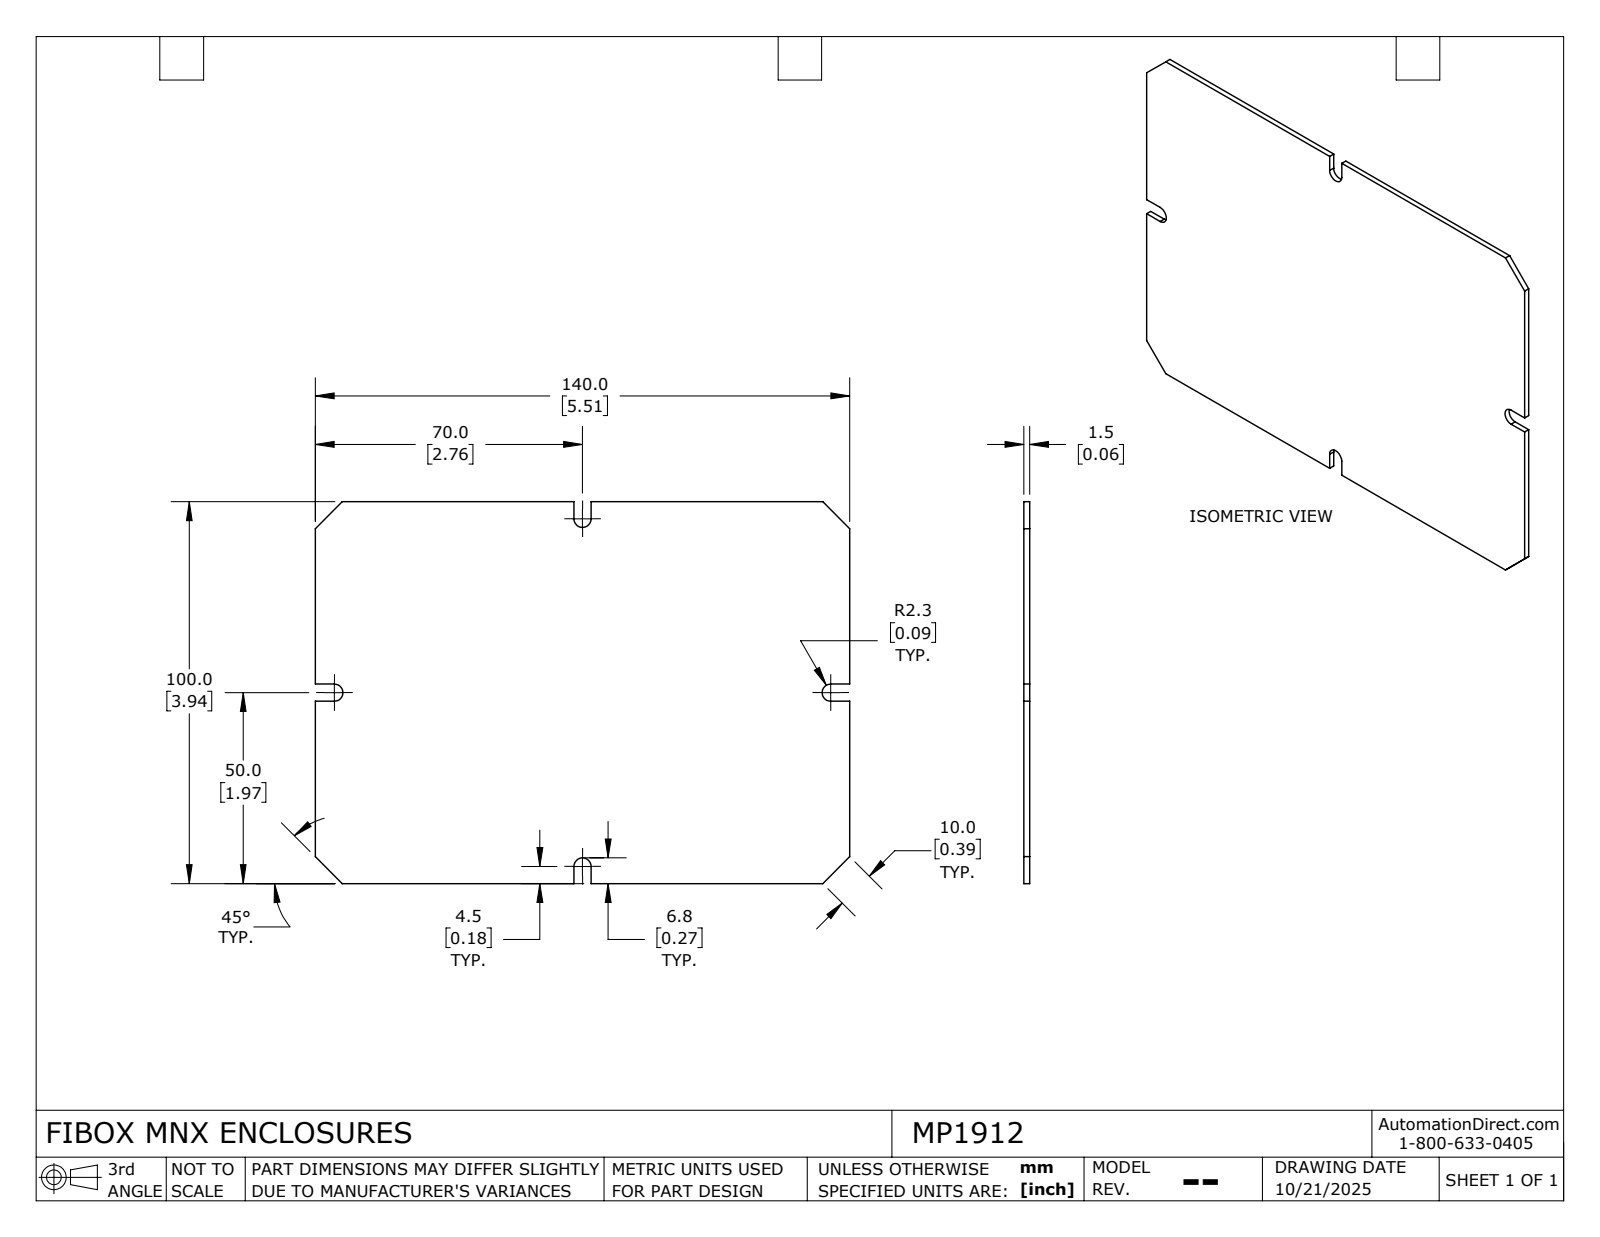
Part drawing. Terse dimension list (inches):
name: MP1912_Default
written by: SolidWorks 2024 (CONFIG_CONTROL_DESIGN)
unit: in
bodies: 1 solid, 26 faces (22 planar, 4 cylindrical, 0 other)
size: 5.512 × 3.937 × 0.059
volume: 1.262 in³; area: 43.92 in²
rounds: 4× R0.089
face distances: 0.059, 3.937, 5.512, 1.88, 2.057, 6.287, 0.177, 2.667, 2.844
